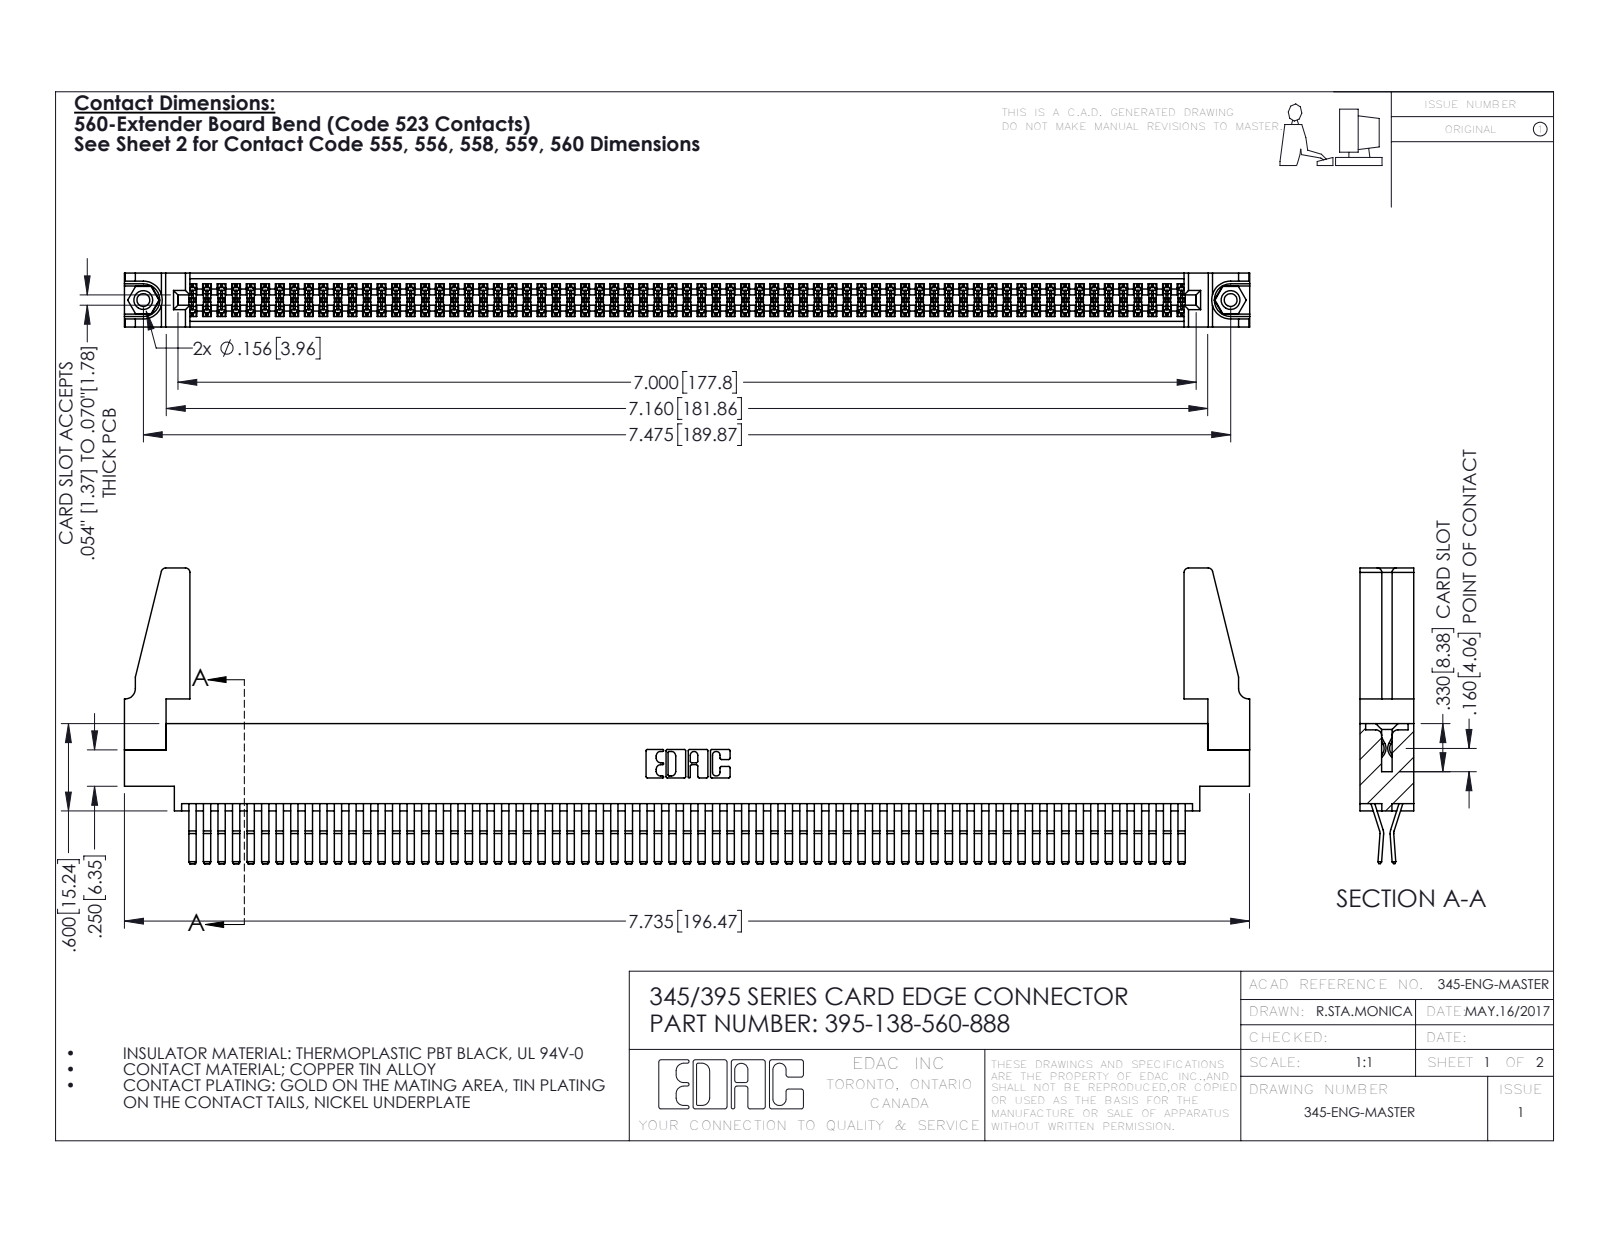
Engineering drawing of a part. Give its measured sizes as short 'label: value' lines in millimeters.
name: 345-220-078_345-220-088; 395-138-560-888; 345-292-001_560 Tail; 345-250-001_345-250-001-102 (+1 more)
written by: SolidWorks 2016 (CONFIG_CONTROL_DESIGN)
unit: mm
bodies: 143 solids, 7430 faces (4710 planar, 2704 cylindrical, 16 other)
size: 196.5 × 51.6 × 9.4
volume: 23 380 mm³; area: 35 870 mm²
holes: 2× ⌀2.3, 2× ⌀3.2, 2× ⌀4, 1× ⌀1.6
bosses: 2× ⌀3.9
rounds: 207× R0.2, 22× R0.3, 8× R0.8, 6× R0.2, 6× R0.8, 3× R0.7, 2× R0.3, 2× R0.4
face distances: 1.8, 0.6, 7.6, 9.4, 2.5, 6.9, 5.1, 5.7, 4.4, 3.8
hole spacings: 6.9, 183.9, 189.9
